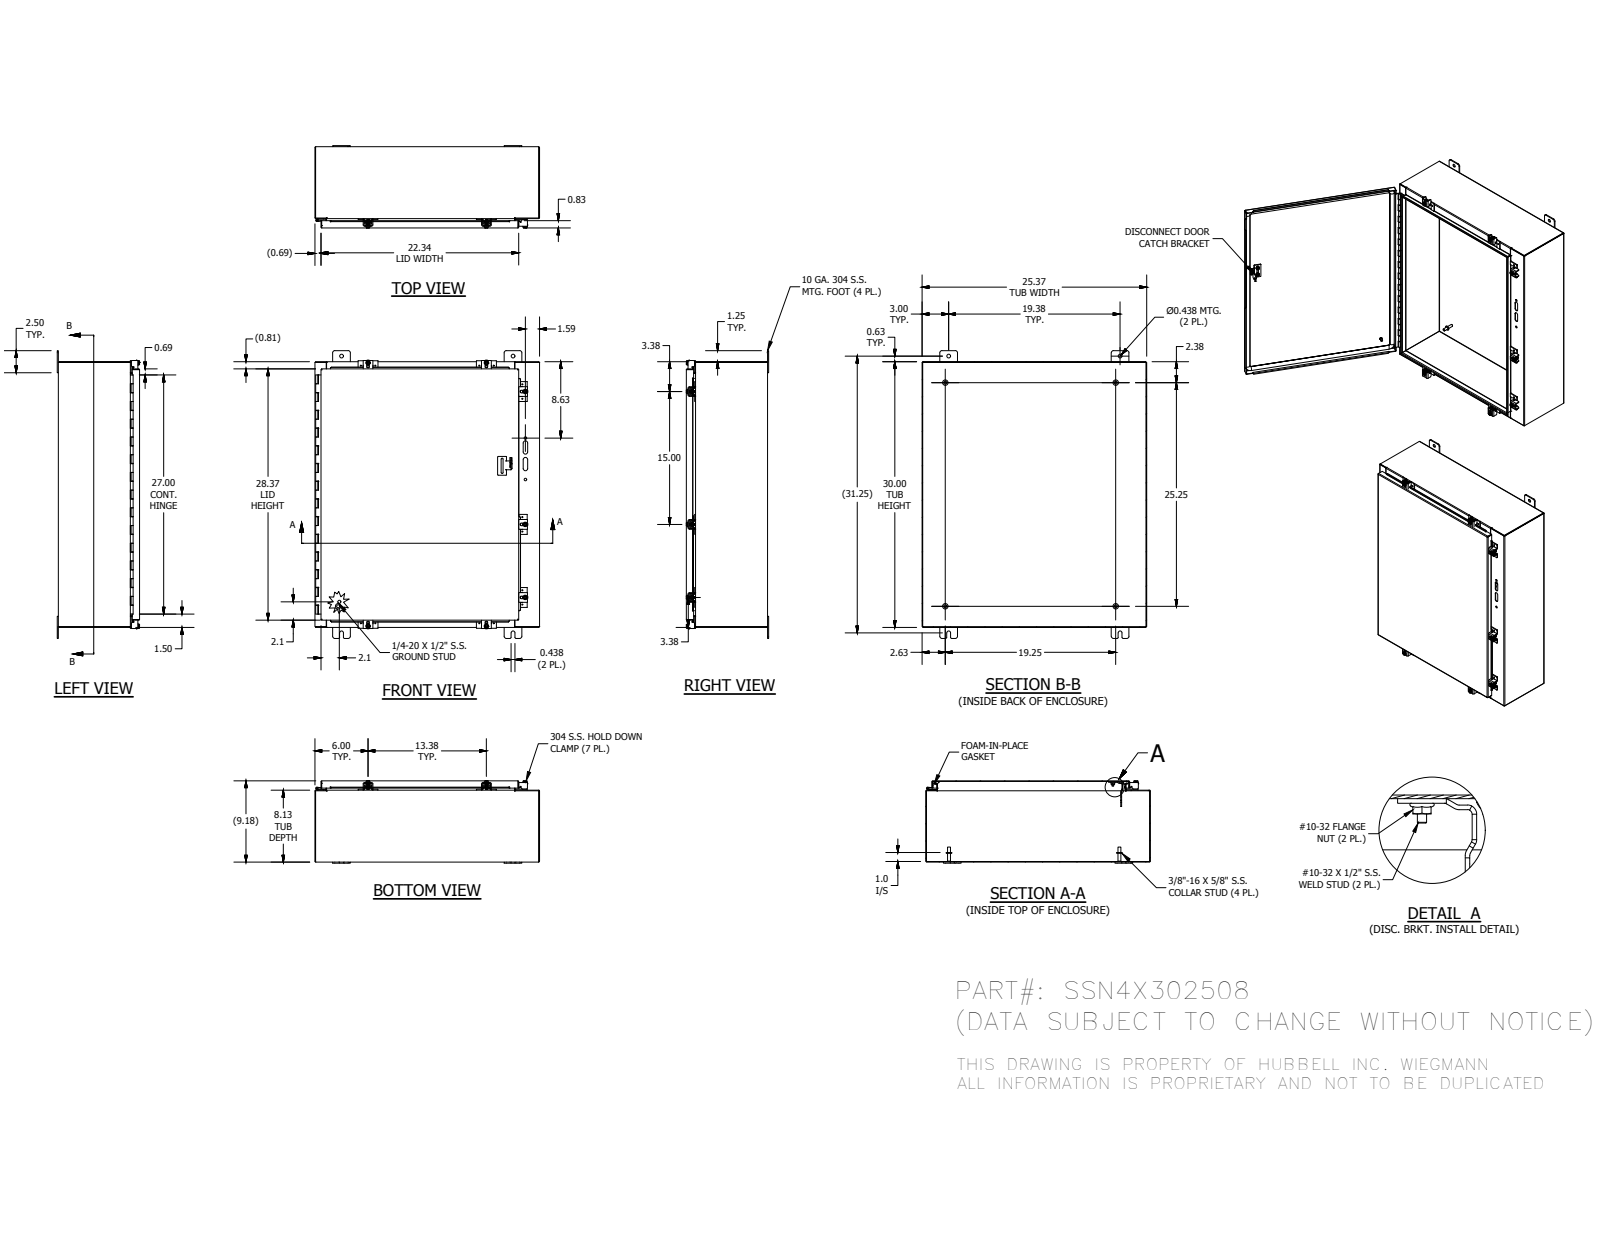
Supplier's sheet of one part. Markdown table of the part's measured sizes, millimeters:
| quantity | value |
| --- | --- |
| part name | SSN4X302508BKP; 38859; 34871; 328139L (+8 more) |
| STEP written by | Autodesk Inventor 2016 (AUTOMOTIVE_DESIGN) |
| units | millimeters |
| bodies | 48 solids, 1715 faces (881 planar, 486 cylindrical, 348 other) |
| overall size | 825.5 × 644.52 × 236.25 |
| volume | 3 624 000 mm³ |
| surface area | 3 691 000 mm² |
| round holes (diameter × count) | 2.79 × 14, 5.36 × 7, 7.16 × 7, 11.13 × 4, 3.17 × 2, 3.96 × 2, 7.14 × 2 |
| round bosses / shafts (diameter × count) | 15.88 × 11, 6.35 × 9, 13.21 × 7, 8.89 × 7, 5.04 × 7, 0.76 × 5, 8.38 × 4, 8.56 × 3 |
| partial cylindrical surfaces (radius × count) | 0.76 × 57, 6.35 × 31, 0.79 × 27, 2.67 × 23, 3.17 × 21, 3.62 × 14, 1.59 × 11, 1.35 × 10 |
| main face-to-face distances | 1.88, 231.19, 229.31, 233.07, 760.12, 1.87, 204.5, 26.69, 644.52, 642.64 |
| hole center spacings | 22.26, 747.39, 41.27, 360.46, 381, 339.72, 738.76, 739.91 |
